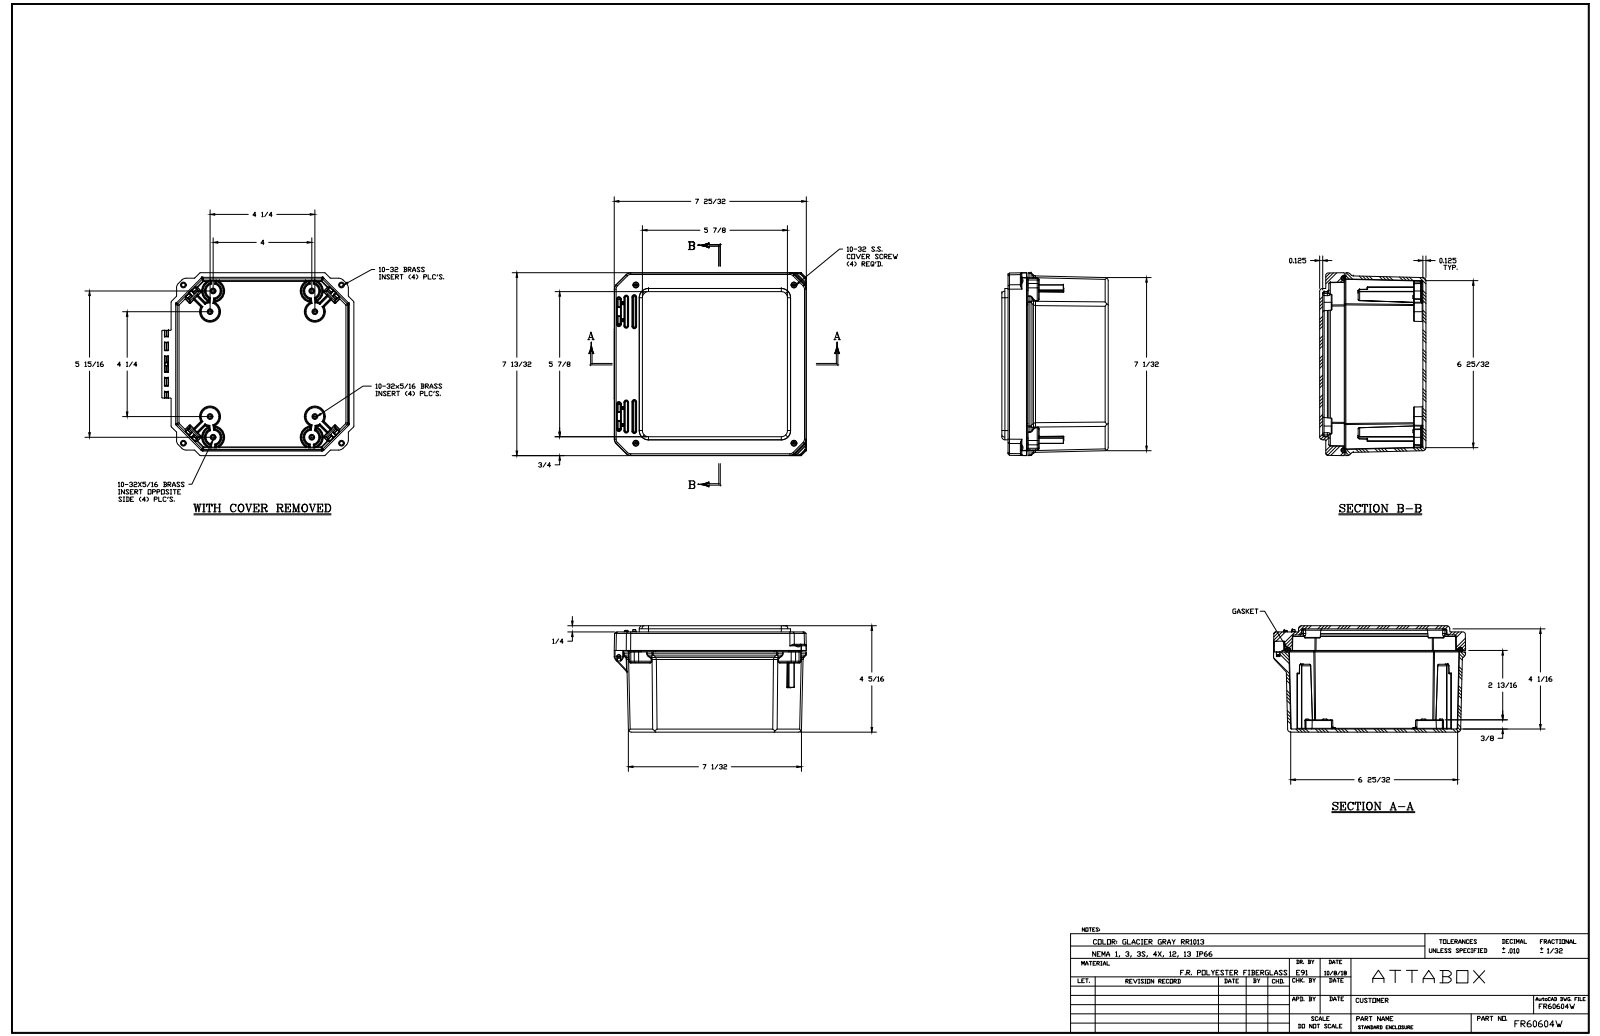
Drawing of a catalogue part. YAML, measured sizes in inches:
part_name: "FR60604W"
step_written_by: "SolidWorks 2018 (AUTOMOTIVE_DESIGN)"
units: inches
bodies: {solids: 23, faces: 1969, planar: 648, cylindrical: 709, other: 612}
overall_size: [7.79, 7.417, 4.31]
volume: 37.58
surface_area: 500.1
round_holes:
  - {diameter: 0.156, count: 12}
  - {diameter: 0.152, count: 8}
  - {diameter: 0.252, count: 4}
  - {diameter: 0.253, count: 4}
  - {diameter: 0.219, count: 2}
  - {diameter: 0.227, count: 2}
  - {diameter: 0.313, count: 2}
  - {diameter: 0.137, count: 1}
round_bosses_or_shafts:
  - {diameter: 0.246, count: 12}
  - {diameter: 0.87, count: 4}
  - {diameter: 0.45, count: 4}
  - {diameter: 0.199, count: 4}
  - {diameter: 0.435, count: 1}
  - {diameter: 0.435, count: 1}
partial_cylinders:
  - {radius: 0.01, count: 109}
  - {radius: 0.005, count: 80}
  - {radius: 0.02, count: 63}
  - {radius: 0.03, count: 45}
  - {radius: 0.03, count: 24}
  - {radius: 0.09, count: 24}
  - {radius: 0.096, count: 22}
  - {radius: 0.125, count: 22}
face_to_face_distances: [0.125, 4.185, 4.31, 4.061, 0.25, 0.124, 0.125, 3.935, 0.375, 4.06]
hole_center_spacings: [5.441, 1.231, 5.759, 0.849, 1.531, 4.209, 4.25, 5.018]
